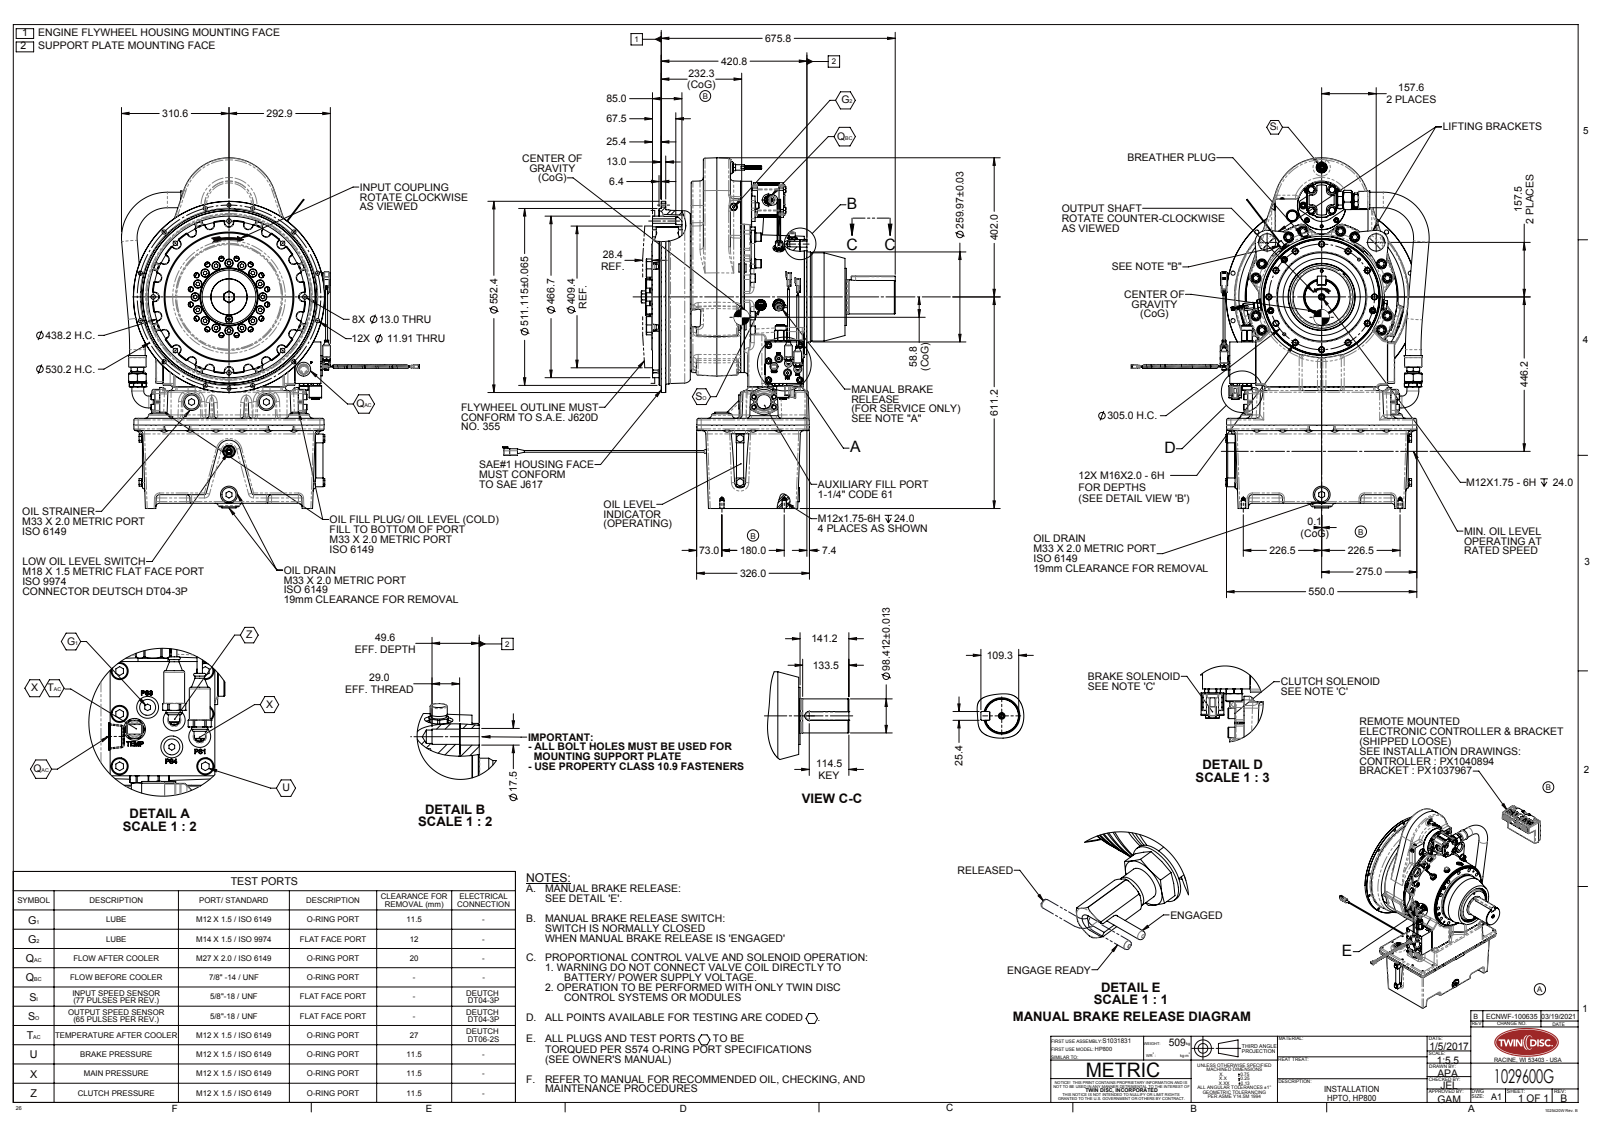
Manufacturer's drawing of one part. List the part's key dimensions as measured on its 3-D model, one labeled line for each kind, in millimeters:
Part name (STEP PRODUCT): 1029600G
STEP written by: SolidWorks 2019 (AUTOMOTIVE_DESIGN)
Units: millimetres
Bodies: 0 solids, 3177 faces (1417 planar, 961 cylindrical, 799 other)
Overall size (bounding box): 1134.48 × 1013.21 × 860.67
Round holes (diameter × count): ⌀14 ×21, ⌀8.5 ×20, ⌀24 ×18, ⌀11.91 ×12, ⌀17.5 ×12, ⌀18 ×9, ⌀13 ×8, ⌀49 ×6, ⌀12 ×5, ⌀30 ×5, ⌀34 ×3, ⌀8 ×2
Round bosses / shafts (diameter × count): ⌀24 ×13, ⌀16 ×7, ⌀40.8 ×6, ⌀16.66 ×4, ⌀30.15 ×3, ⌀28 ×3, ⌀25.4 ×3, ⌀20 ×3
Partial cylindrical surfaces — rounded edges, fillets, slot ends (radius × count): R5 ×106, R10 ×92, R2.54 ×66, R3 ×34, R12.7 ×28, R13.7 ×16, R1.27 ×13, R12.5 ×12
Main face-to-face distances: 10.6, 20.6, 0.6, 10, 180.6, 181.2, 11.2, 13, 27.38, 170.6
Hole centre spacings: 75, 225, 375, 150, 309.23, 86.1, 112.5, 140.26
